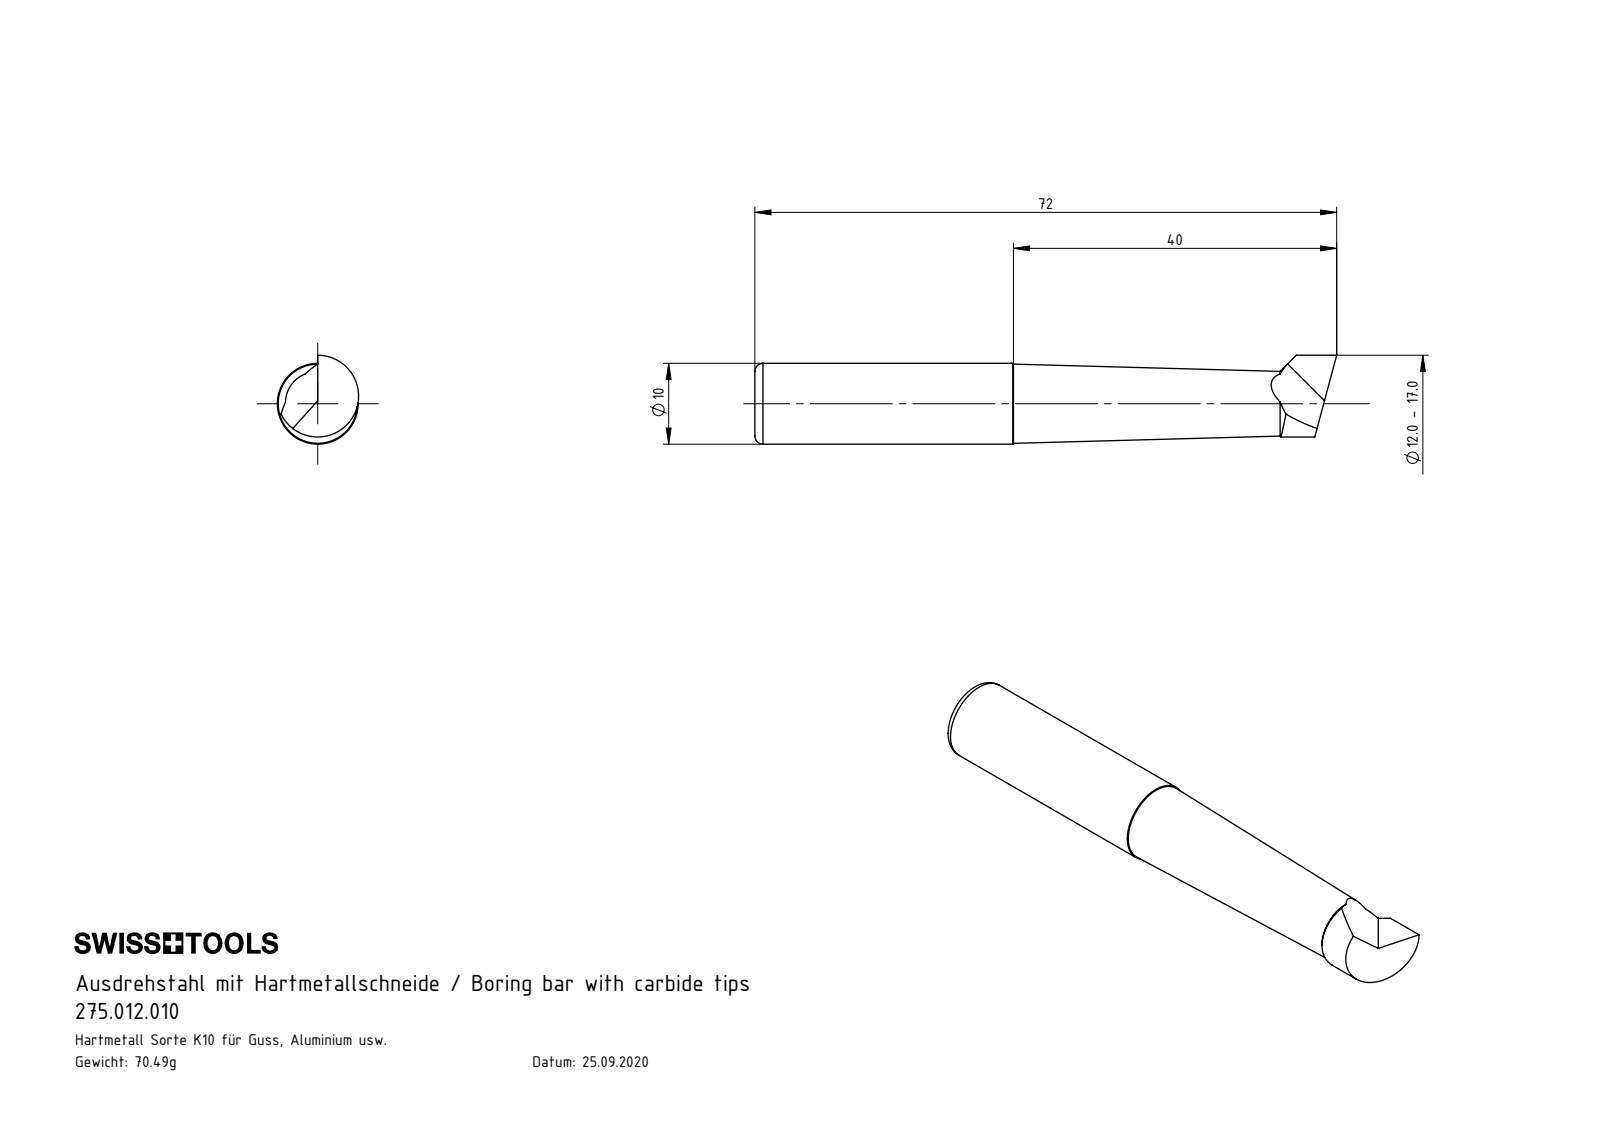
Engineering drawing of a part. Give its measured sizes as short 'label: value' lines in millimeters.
name: 275.012.010
written by: SolidWorks 2022 (CONFIG_CONTROL_DESIGN)
unit: mm
bodies: 1 solid, 16 faces (4 planar, 3 cylindrical, 9 other)
size: 72 × 11 × 10.06
volume: 4 862 mm³; area: 2 217 mm²
bosses: 1× ⌀10
rounds: 1× R5.06
